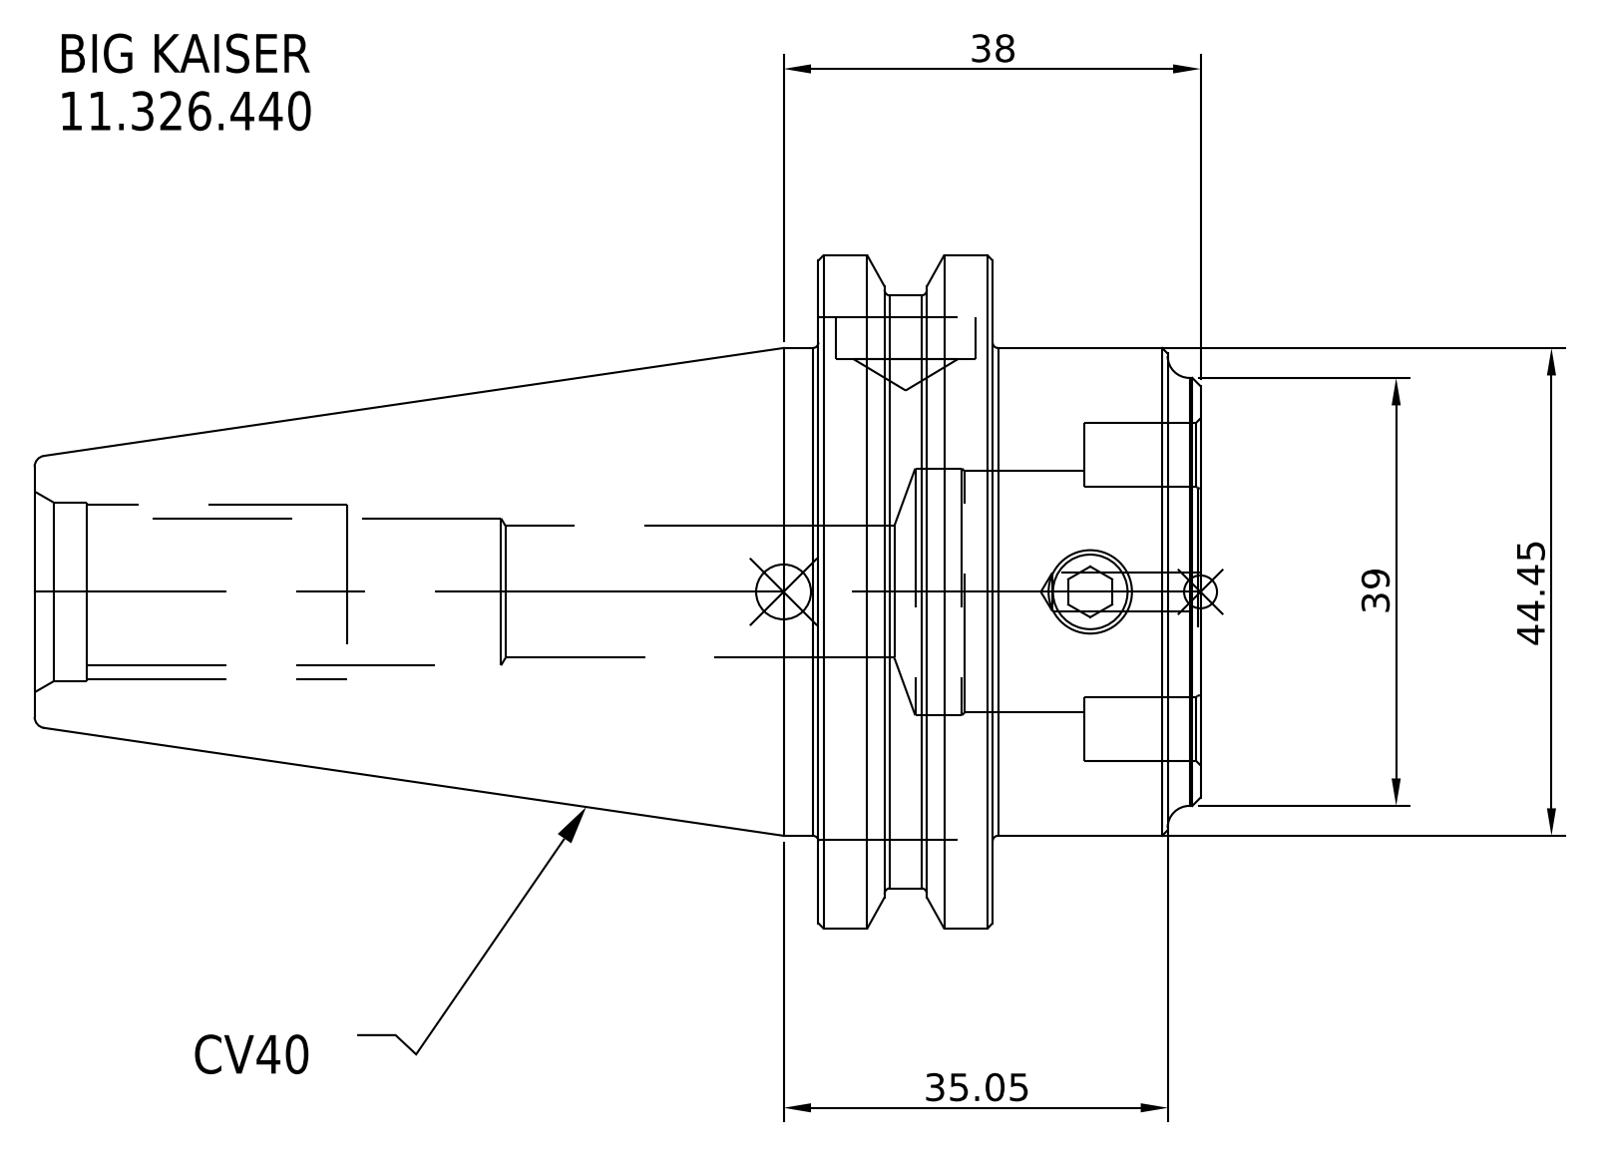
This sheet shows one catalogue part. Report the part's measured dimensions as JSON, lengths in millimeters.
{"part_name": "11_326_440", "step_written_by": "SolidWorks 2021 (CONFIG_CONTROL_DESIGN)", "units": "millimeters", "bodies": {"solids": 1, "faces": 29, "planar": 7, "cylindrical": 12, "other": 10}, "overall_size": [106.25, 63.5, 63.5], "volume_mm3": 145721, "surface_area_mm2": 19572, "round_bosses_or_shafts": [[63.5, 1], [56.36, 1], [44.45, 1], [39, 1]], "face_to_face_distances": [15.88, 18.95, 34.83, 106.25, 87.3, 71.42, 2.95, 16, 31.88, 103.3]}
